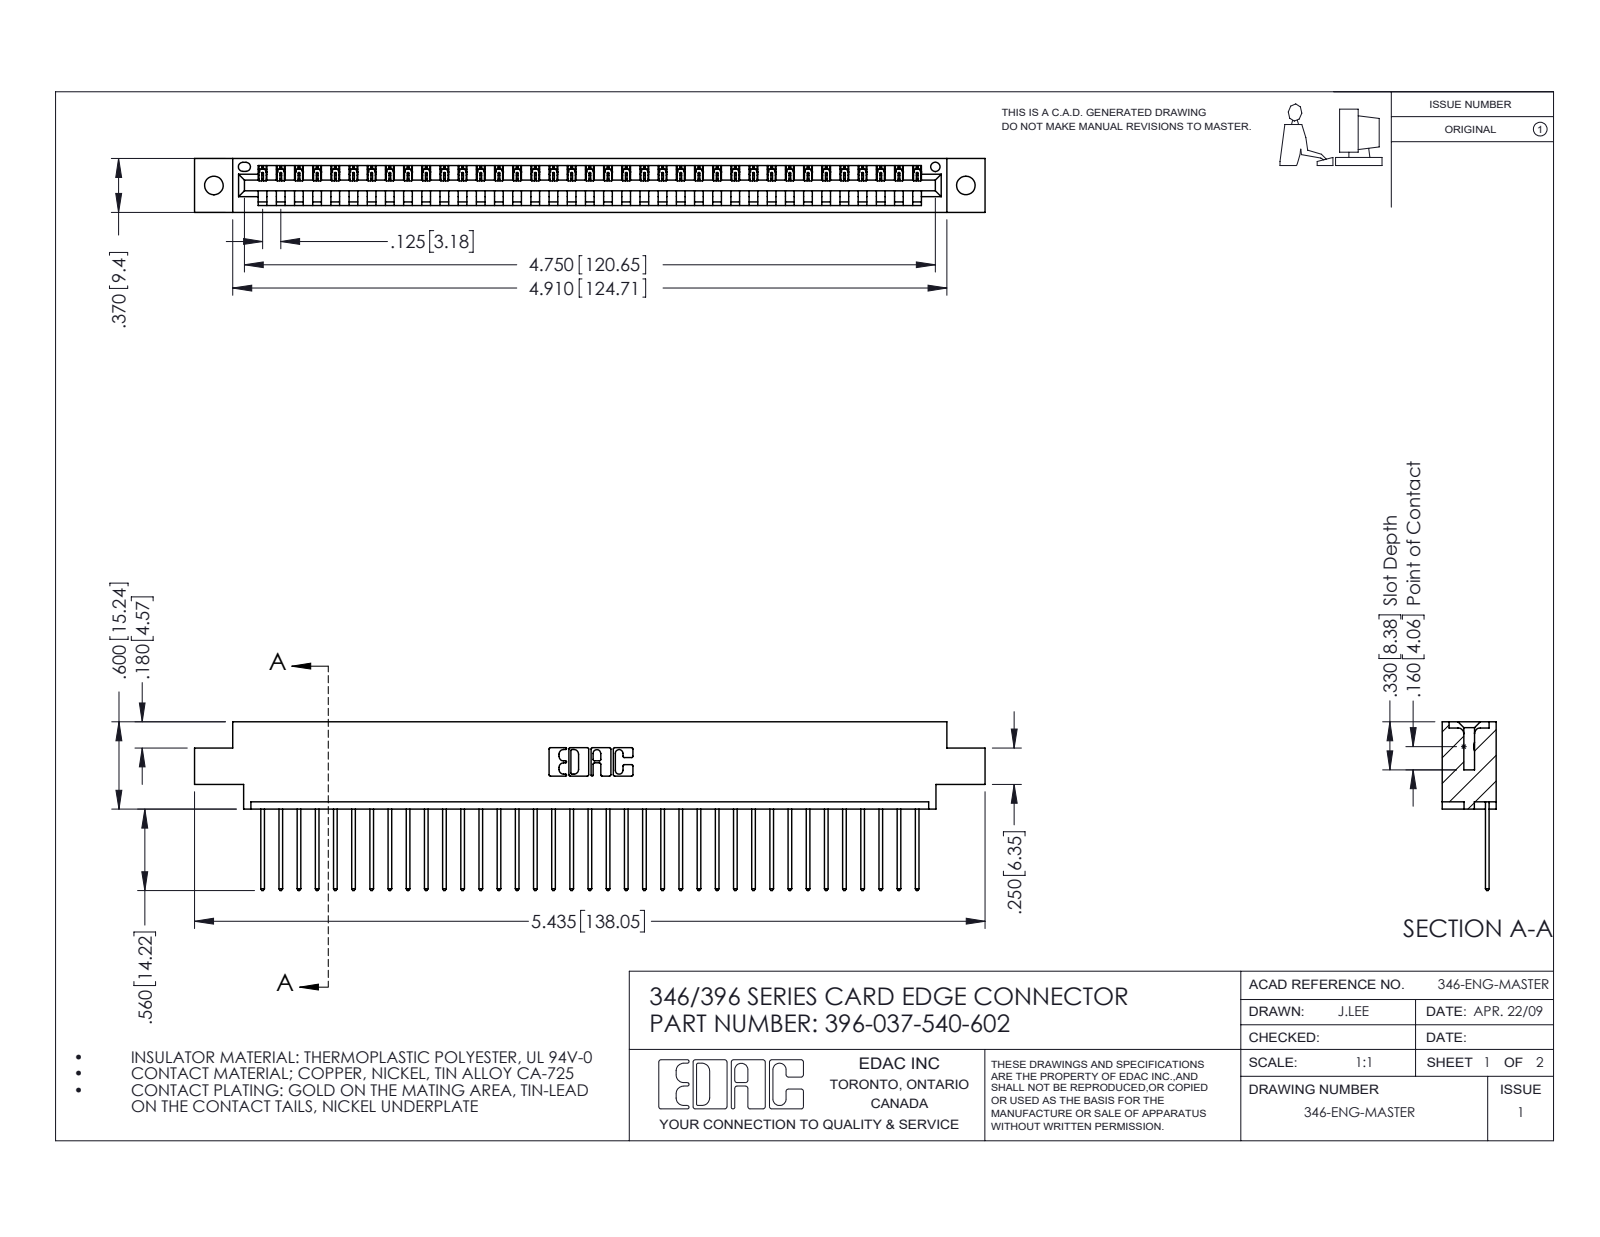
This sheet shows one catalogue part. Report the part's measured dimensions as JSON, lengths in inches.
{"part_name": "396-037-540-602; 346 Part_0.170 Offset - 0.128 Dia; 345-292-001_345-293-140", "step_written_by": "SolidWorks 2016 (CONFIG_CONTROL_DESIGN)", "units": "inches", "bodies": {"solids": 38, "faces": 2272, "planar": 1560, "cylindrical": 712, "other": 0}, "overall_size": [5.435, 1.16, 0.37], "volume_in3": 0.796, "surface_area_in2": 25.57, "round_holes": [[0.128, 2], [0.064, 1]], "partial_cylinders_radius": [[0.006, 74], [0.01, 74], [0.01, 22], [0.007, 6], [0.031, 6], [0.026, 3], [0.031, 2], [0.04, 2]], "face_to_face_distances": [0.048, 0.322, 0.37, 0.25, 0.072, 0.298, 0.025, 0.148, 0.222, 0.1], "hole_center_spacings": [0.246, 4.961, 5.17]}
